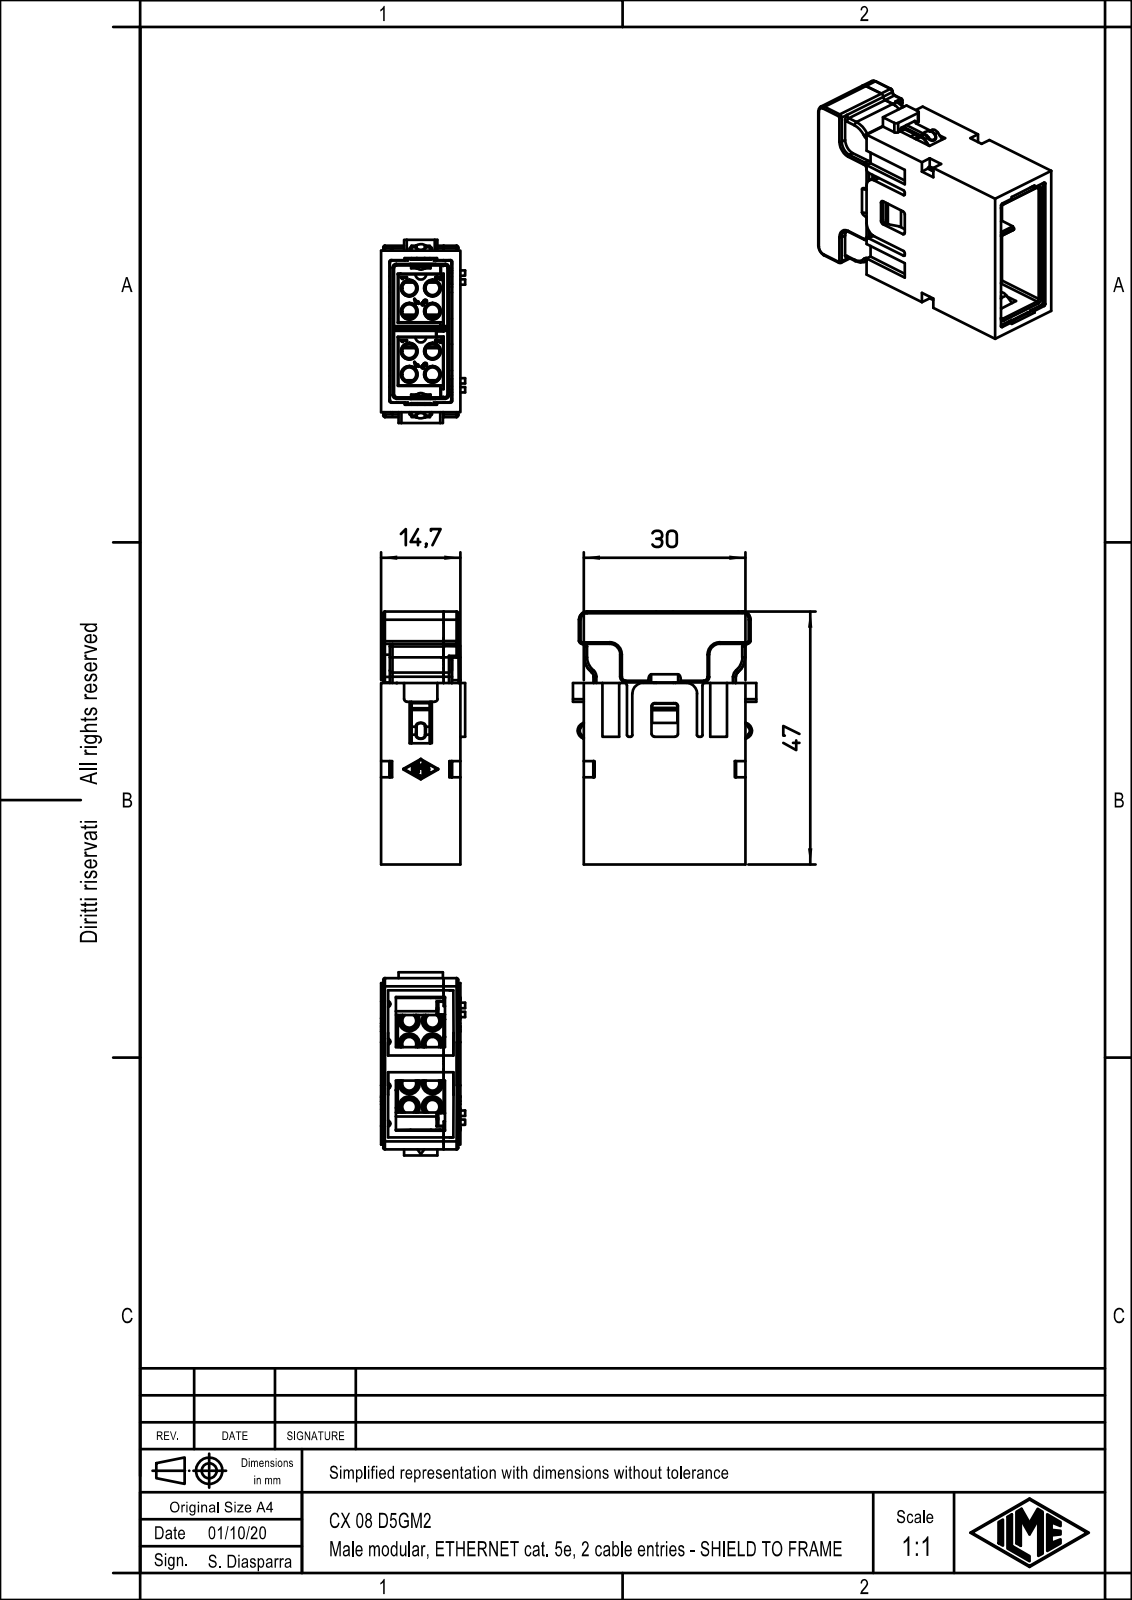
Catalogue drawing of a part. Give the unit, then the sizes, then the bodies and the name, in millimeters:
Units: millimetres
Overall size (bounding box): 46.95 × 34 × 15.6
Round holes (diameter × count): ⌀2.6 ×10, ⌀2.25 ×2, ⌀5 ×2, ⌀1.4 ×1
Round bosses / shafts (diameter × count): ⌀4.7 ×2, ⌀1.9 ×2, ⌀1.3 ×1
Partial cylindrical surfaces — rounded edges, fillets, slot ends (radius × count): R0.5 ×50, R0.3 ×40, R1 ×10, R0.4 ×8, R0.65 ×8, R2 ×6, R0.1 ×4, R0.2 ×4
Main face-to-face distances: 1.6, 13.1, 1.55, 13.15, 11.55, 11.5, 11.6, 14.7, 0.4, 1.15
Hole centre spacings: 4.3, 6.08, 11.7, 12.47, 7.4, 8.56, 16, 16.57
Volume: 15 103 mm³ · Surface area: 12 929 mm²
Bodies: 1 solid, 691 faces (407 planar, 215 cylindrical, 69 other)
Part name (STEP PRODUCT): CX 08 D5GM2
STEP written by: Creo Elements/Direct Modeling 20.1B 02-Apr-2019 (C) Parametric Technology GmbH (AUTOMOTIVE_DESIGN)
